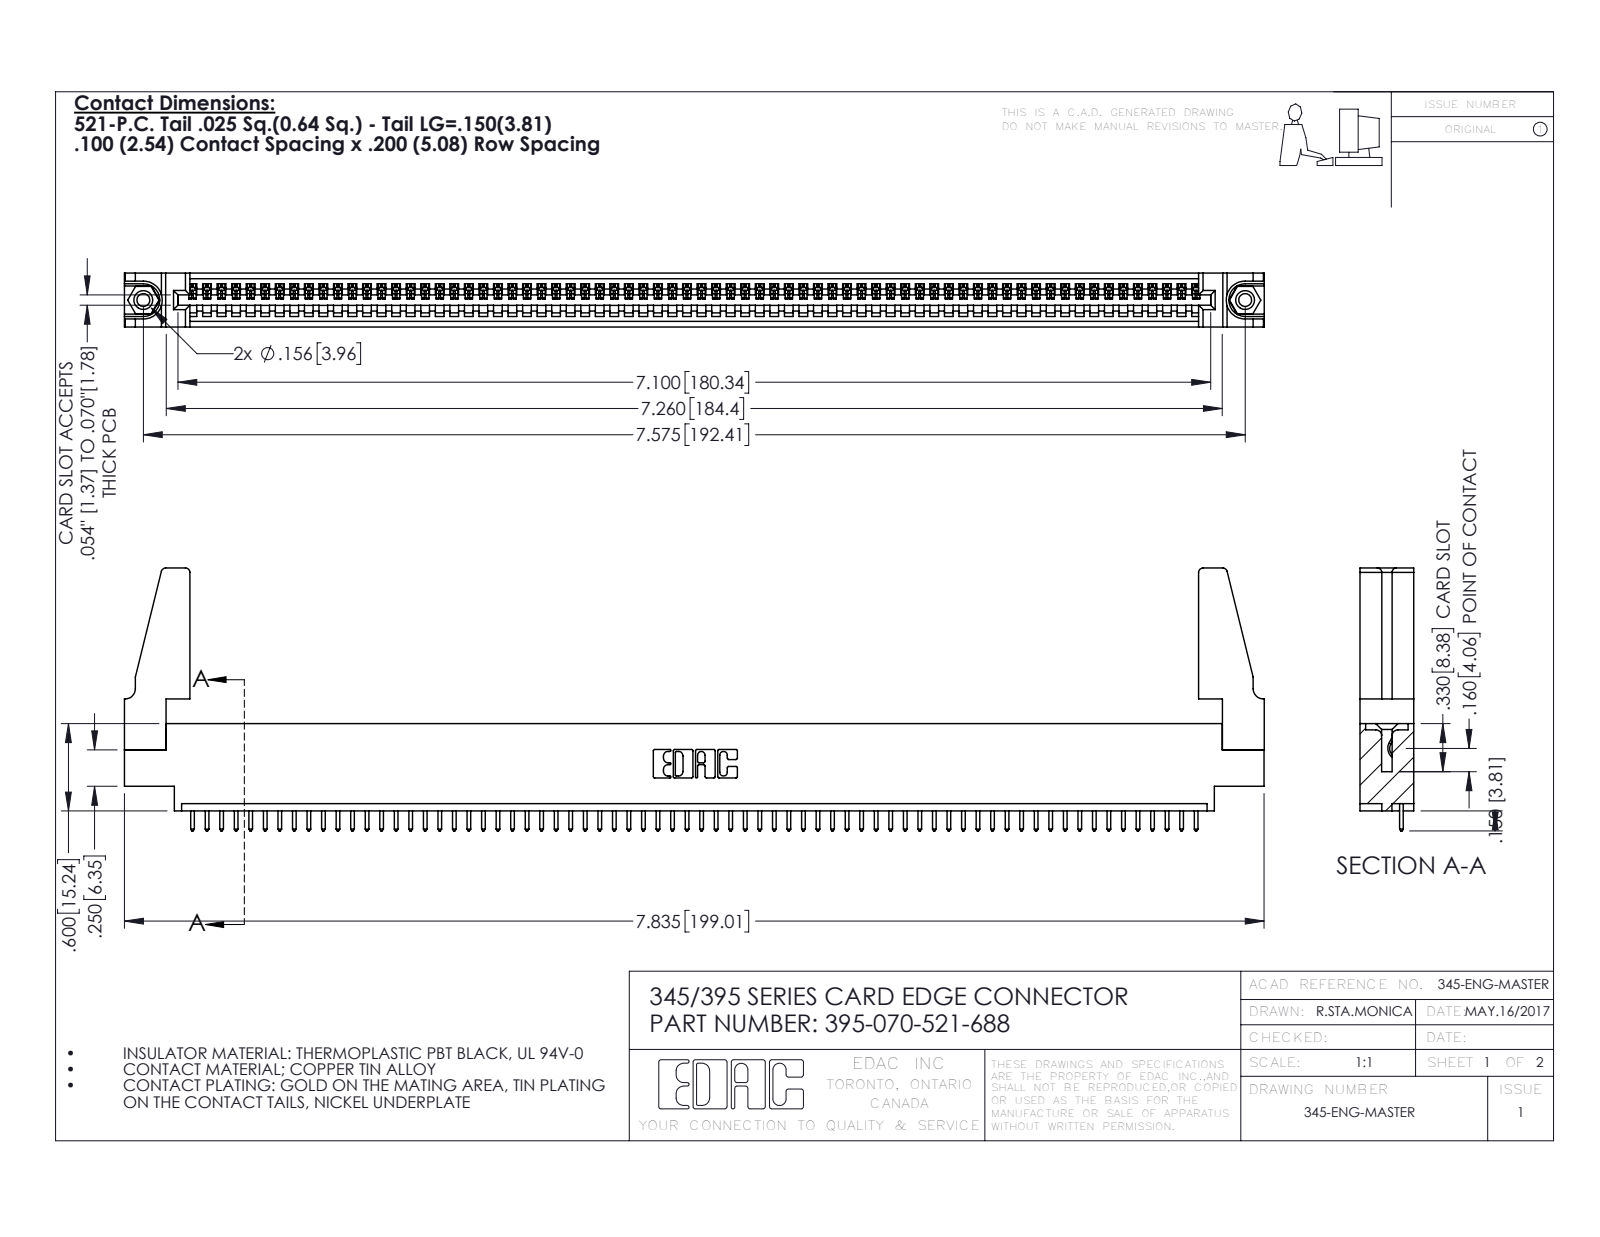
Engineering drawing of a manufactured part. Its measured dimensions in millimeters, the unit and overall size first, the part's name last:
Units: millimetres
Overall size (bounding box): 199 × 45.9 × 9.4
Round holes (diameter × count): ⌀2.3 ×2, ⌀3.2 ×2, ⌀4 ×2, ⌀1.6 ×1
Round bosses / shafts (diameter × count): ⌀3.9 ×2
Partial cylindrical surfaces — rounded edges, fillets, slot ends (radius × count): R0.2 ×140, R0.3 ×140, R0.3 ×22, R0.8 ×8, R0.2 ×6, R0.8 ×6, R0.7 ×3, R0.8 ×2
Main face-to-face distances: 1.8, 7.6, 9.4, 5.1, 2.5, 6.9, 0.6, 5.7, 4.4, 3.8
Hole centre spacings: 6.9, 186.4, 192.4
Volume: 22 070 mm³ · Surface area: 27 870 mm²
Bodies: 75 solids, 4314 faces (2956 planar, 1342 cylindrical, 16 other)
Part name (STEP PRODUCT): 345-250-001_345-250-001-102; 345 Part_0.170 Offset - 0.156 Dia-TH; 395-070-521-688; 345-292-001_345-293-121 (+1 more)
STEP written by: SolidWorks 2016 (CONFIG_CONTROL_DESIGN)
